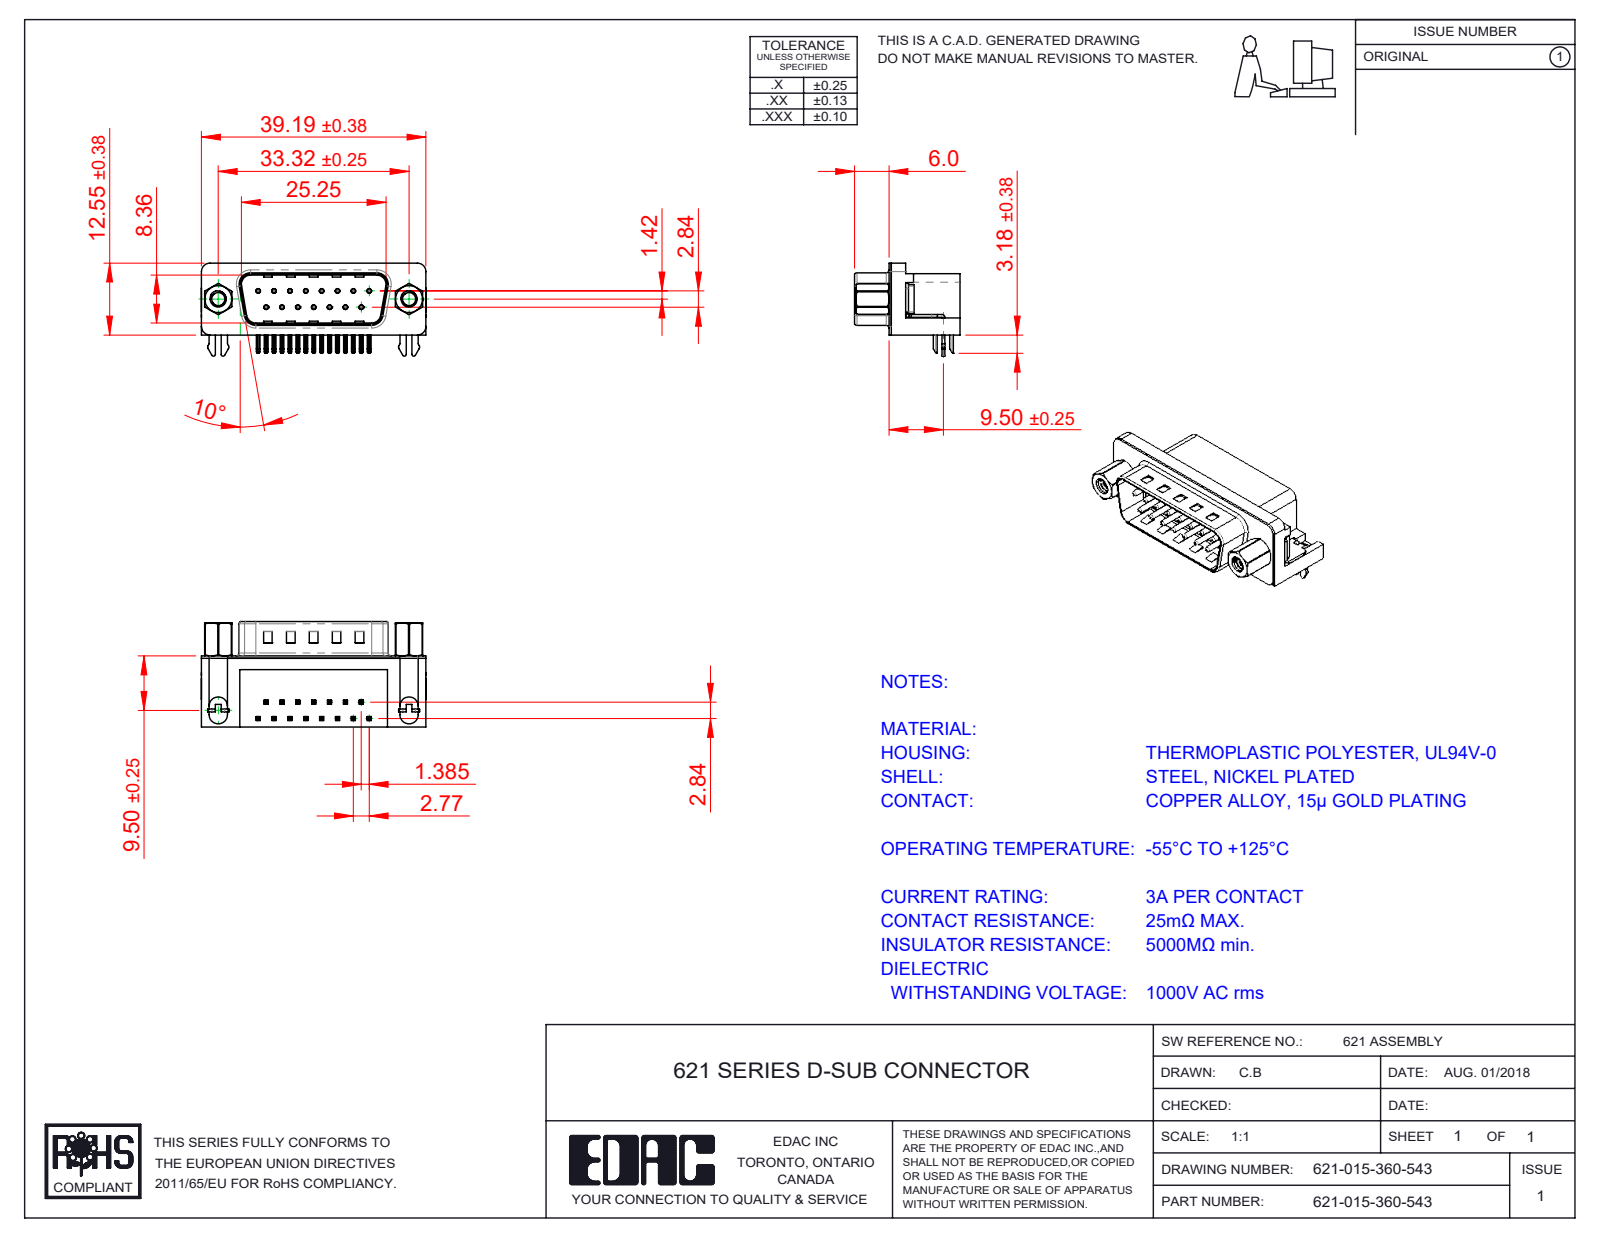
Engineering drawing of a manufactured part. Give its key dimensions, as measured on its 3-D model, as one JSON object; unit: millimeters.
{"part_name": "621 4 Prong Board Lock; 621 4-40 Threaded Rivet; 621 Shell_15 Socket; 621 Contact Top (+4 more)", "step_written_by": "SolidWorks 2016 (CONFIG_CONTROL_DESIGN)", "units": "millimeters", "bodies": {"solids": 23, "faces": 1723, "planar": 957, "cylindrical": 523, "other": 243}, "overall_size": [39.22, 18.4, 16.25], "volume_mm3": 4638, "surface_area_mm2": 6208, "round_holes": [[0.35, 15], [0.8, 15], [2, 2], [2.26, 2], [2.29, 2], [4, 2], [4.8, 2], [5, 2]], "round_bosses_or_shafts": [[0.75, 15], [4.9, 2], [4.75, 2], [3.9, 2], [3, 2], [2.79, 2]], "partial_cylinders_radius": [[0.25, 72], [0.12, 30], [1, 16], [0.5, 9], [1.6, 8], [1.5, 6], [0.9, 4], [2, 4]], "face_to_face_distances": [0.4, 12, 10.35, 12.4, 2.1, 10.46, 1.7, 10.86, 8.76, 9.5], "hole_center_spacings": [3.16, 2.77, 5.54, 8.31, 11.08, 5.03, 5.04, 7.48]}
